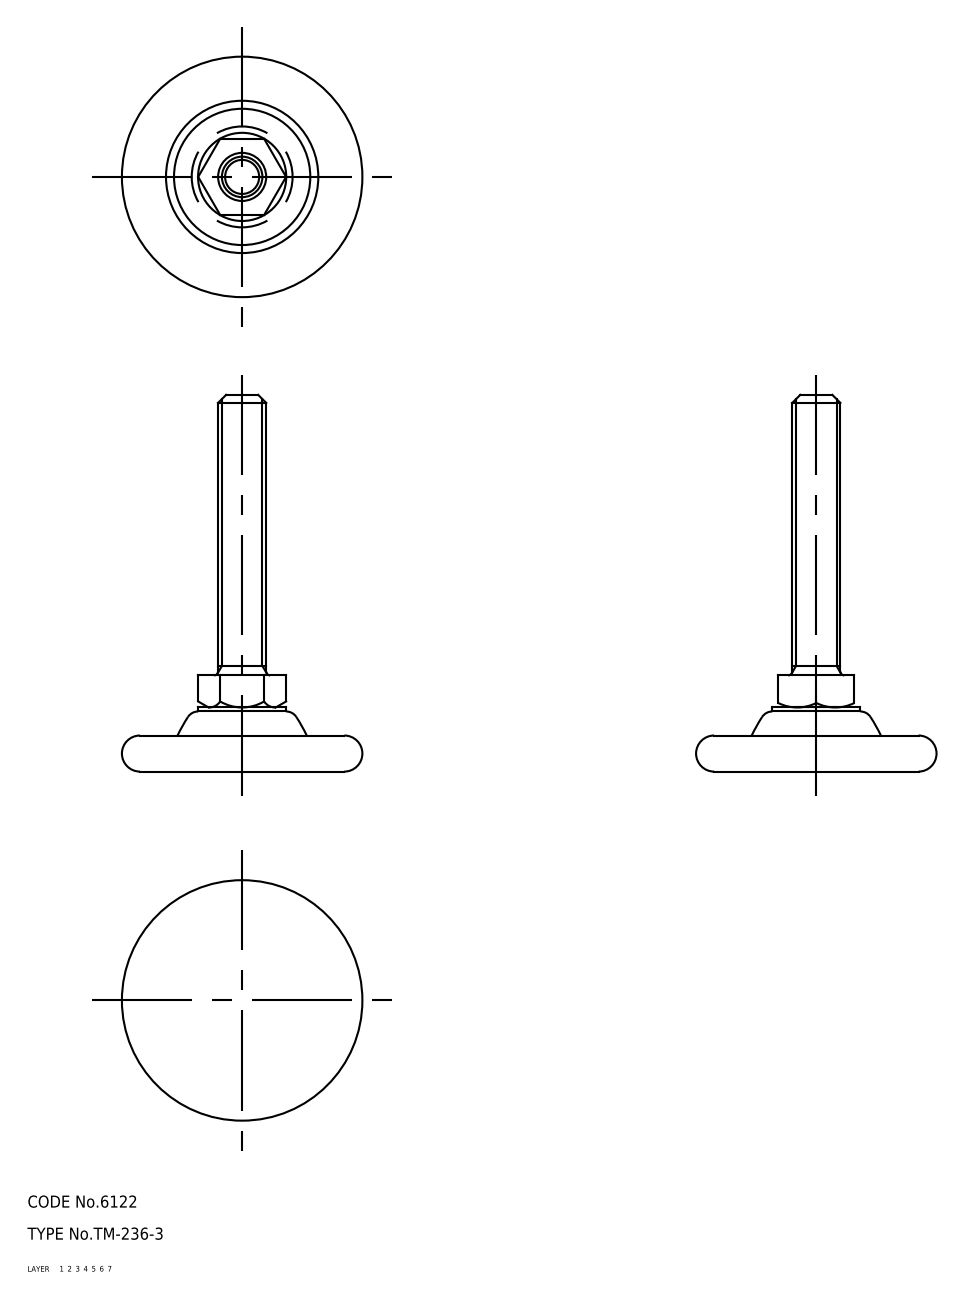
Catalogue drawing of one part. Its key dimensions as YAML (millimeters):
part_name: "67112991; 67113004; 67113017; 67113030"
step_written_by: "CADfix (AUTOMOTIVE_DESIGN)"
units: millimeters
bodies: {solids: 4, faces: 60, planar: 0, cylindrical: 0, other: 60}
overall_size: [94, 60, 60]
volume: 31901
surface_area: 19631
